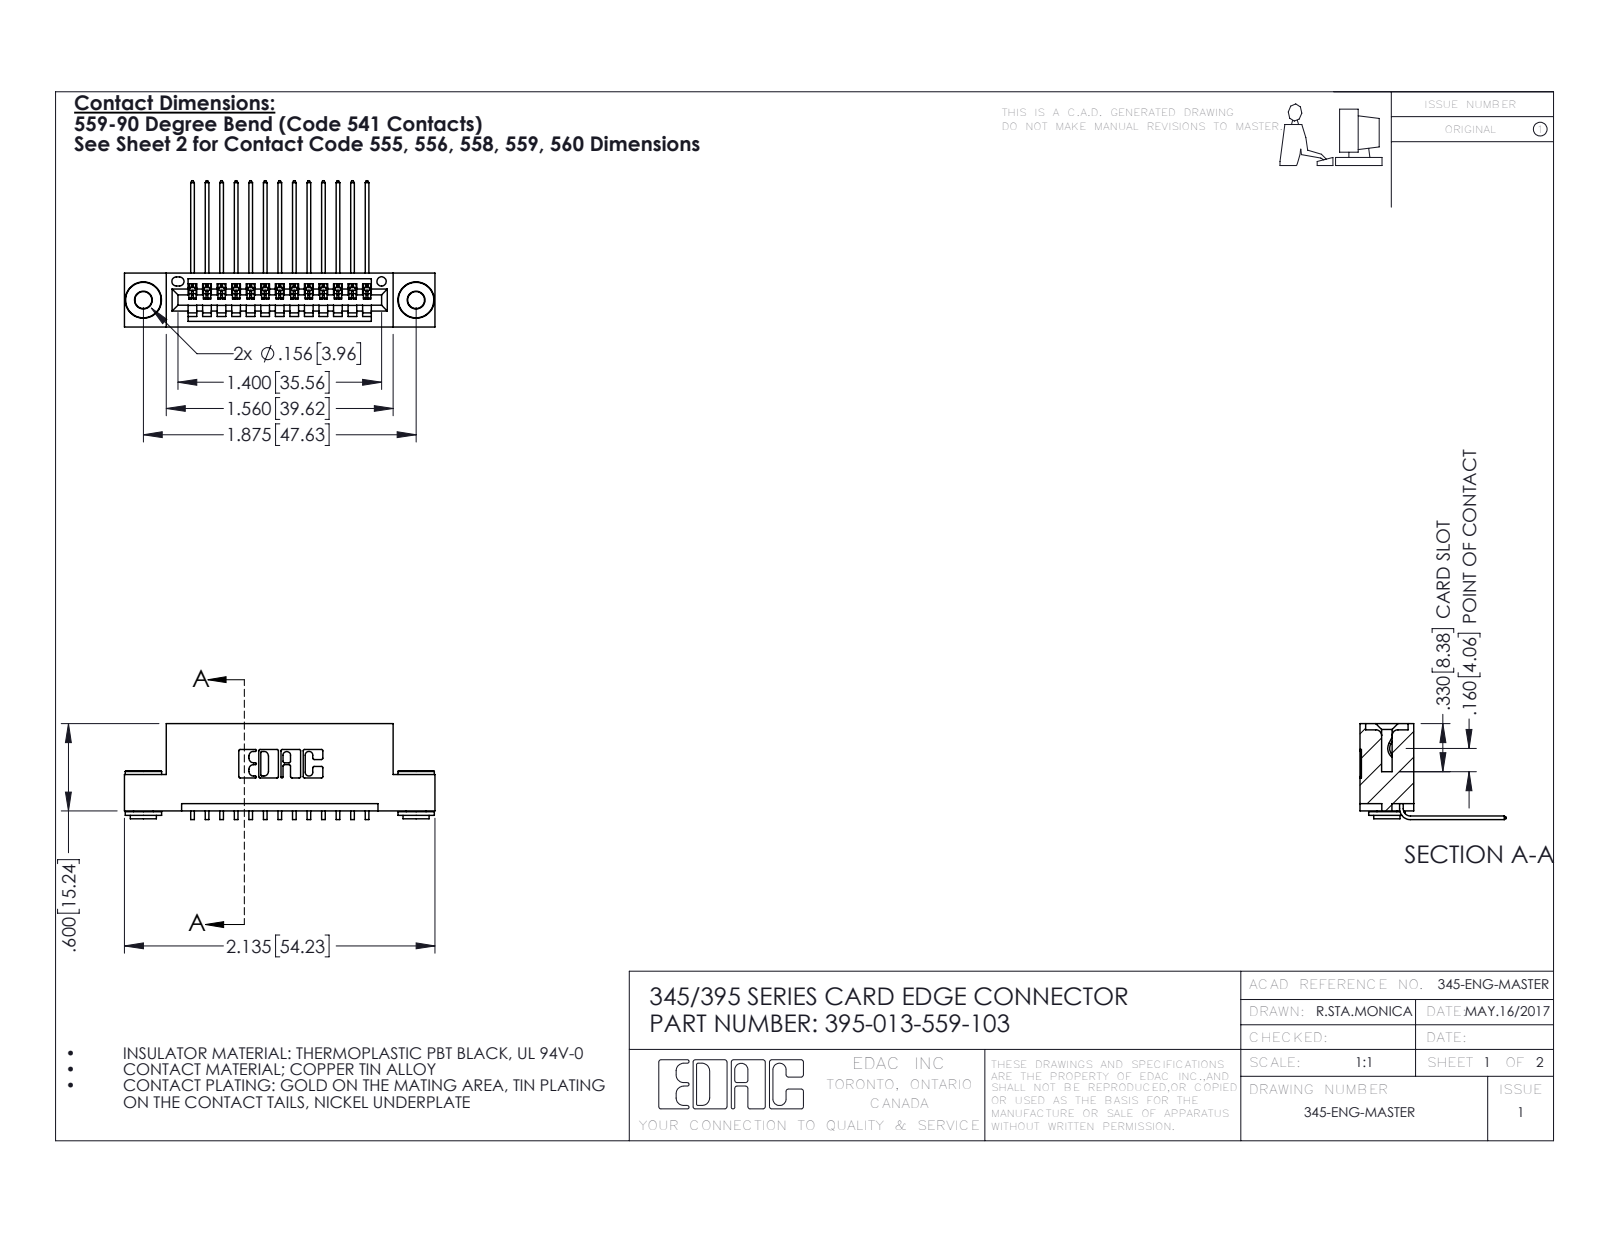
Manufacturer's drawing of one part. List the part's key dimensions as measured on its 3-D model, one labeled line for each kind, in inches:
Part name (STEP PRODUCT): 345-292-001_558 559 Tail - 1; 395-013-559-103; 345-250-002_345-250-002-102; 345 Part_Flush Mounting Lugs - 0.156 Dia-TH
STEP written by: SolidWorks 2016 (CONFIG_CONTROL_DESIGN)
Units: inches
Bodies: 16 solids, 944 faces (636 planar, 300 cylindrical, 8 other)
Overall size (bounding box): 2.135 × 1.005 × 0.659
Volume: 0.304 in³ · Surface area: 10.37 in²
Round holes (diameter × count): ⌀0.116 ×2, ⌀0.156 ×2, ⌀0.064 ×1
Round bosses / shafts (diameter × count): ⌀0.25 ×2, ⌀0.18 ×2, ⌀0.136 ×2
Partial cylindrical surfaces — rounded edges, fillets, slot ends (radius × count): R0.006 ×26, R0.01 ×22, R0.007 ×6, R0.031 ×6, R0.026 ×3, R0.031 ×2, R0.04 ×2, R0.014 ×1
Main face-to-face distances: 0.2, 0.072, 0.298, 0.37, 0.025, 0.098, 0.272, 0.1, 0.225, 0.3
Hole centre spacings: 0.27, 1.643, 1.875
